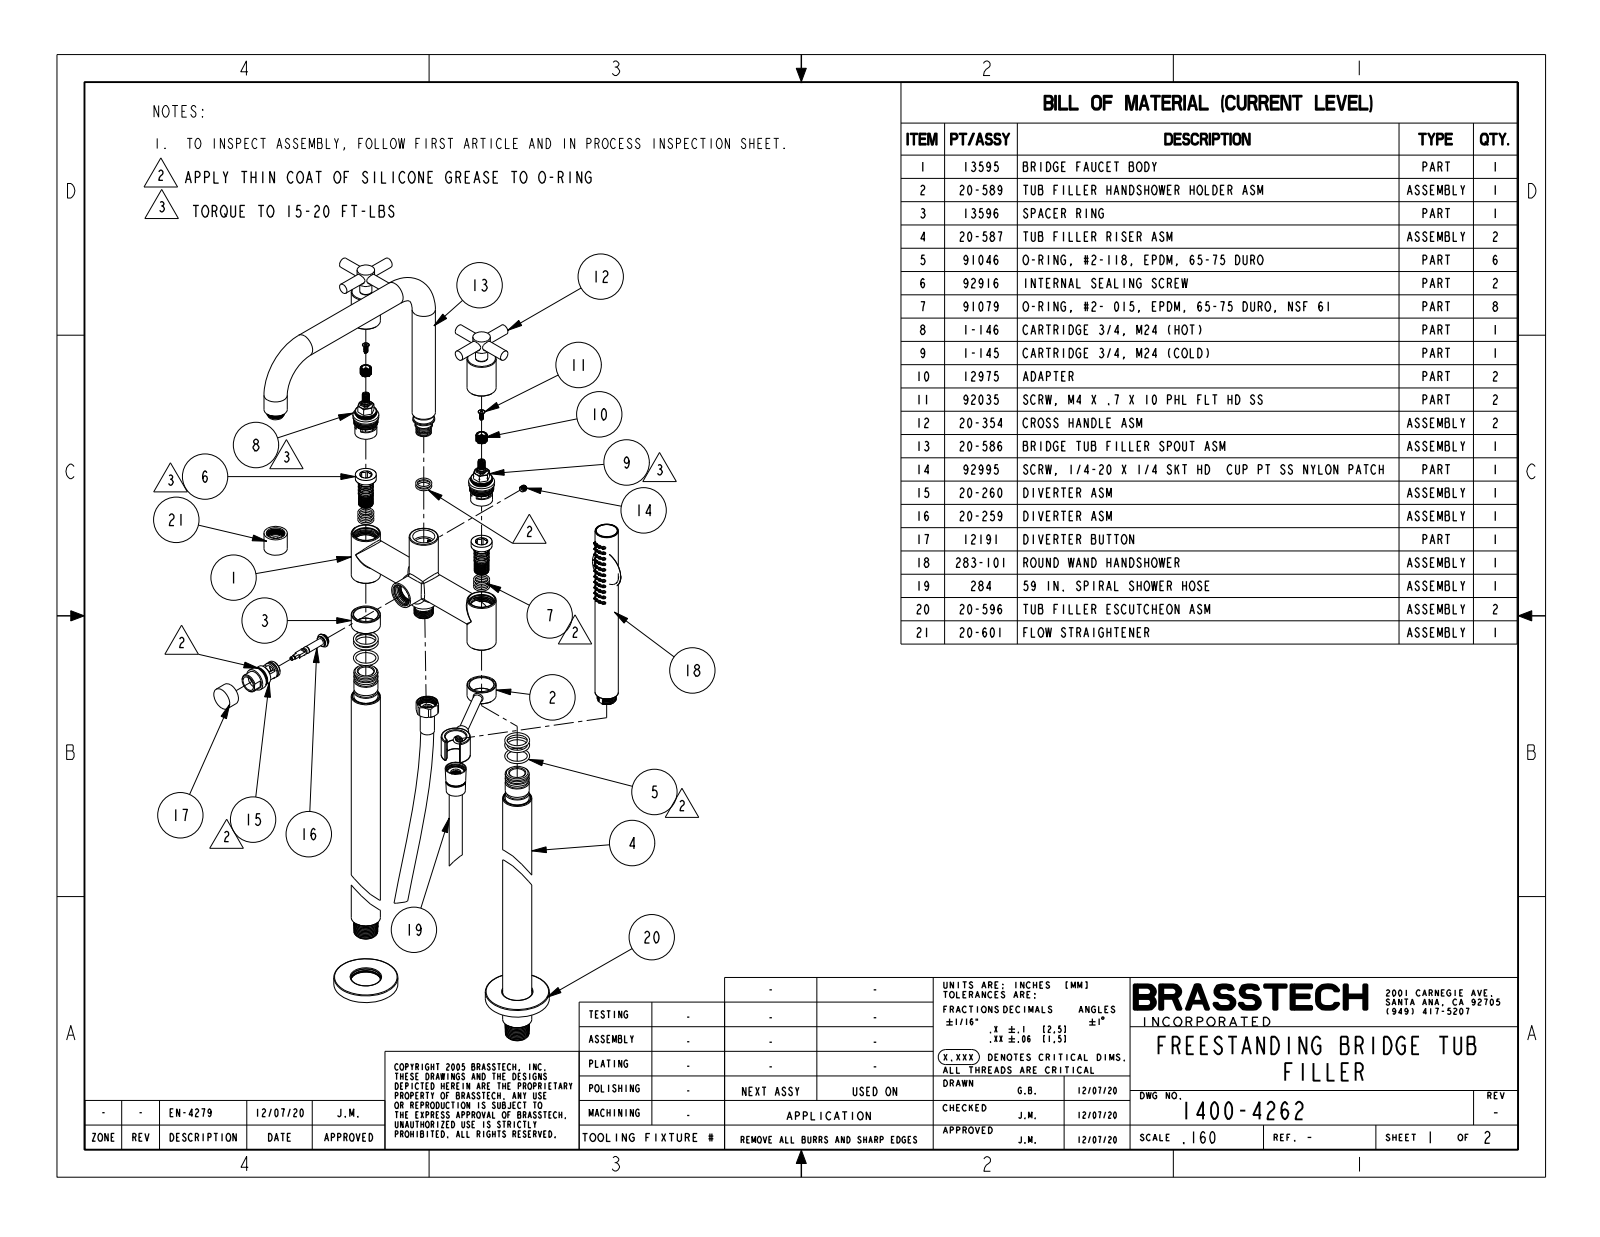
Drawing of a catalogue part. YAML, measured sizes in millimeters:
part_name: "1400-4262"
step_written_by: "CREO PARAMETRIC BY PTC INC, 2019352 (CONFIG_CONTROL_DESIGN)"
units: millimeters
bodies: {solids: 4, faces: 1421, planar: 220, cylindrical: 466, other: 735}
overall_size: [1018.2, 343.2, 276.2]
volume: 2106000
surface_area: 331100
round_holes:
  - {diameter: 3.6, count: 44}
  - {diameter: 3, count: 1}
  - {diameter: 15.4, count: 1}
  - {diameter: 17.6, count: 1}
  - {diameter: 23.9, count: 1}
round_bosses_or_shafts:
  - {diameter: 31.8, count: 5}
  - {diameter: 25.4, count: 4}
  - {diameter: 19.1, count: 3}
  - {diameter: 14.2, count: 3}
  - {diameter: 11.3, count: 3}
  - {diameter: 69.9, count: 2}
  - {diameter: 29.2, count: 2}
  - {diameter: 13.3, count: 2}
partial_cylinders:
  - {radius: 0.8, count: 6}
  - {radius: 2.5, count: 4}
  - {radius: 7.6, count: 1}
  - {radius: 8.6, count: 1}
  - {radius: 9.3, count: 1}
  - {radius: 10.4, count: 1}
  - {radius: 11.4, count: 1}
  - {radius: 12.5, count: 1}
face_to_face_distances: [9.7, 823.3, 813.7, 34.9, 852.1, 842.4, 28.7, 824.6, 814.9, 1.2]
hole_center_spacings: [15.3, 8.5, 4.3, 22.5, 29.8, 14.7, 17.1, 7.4]
